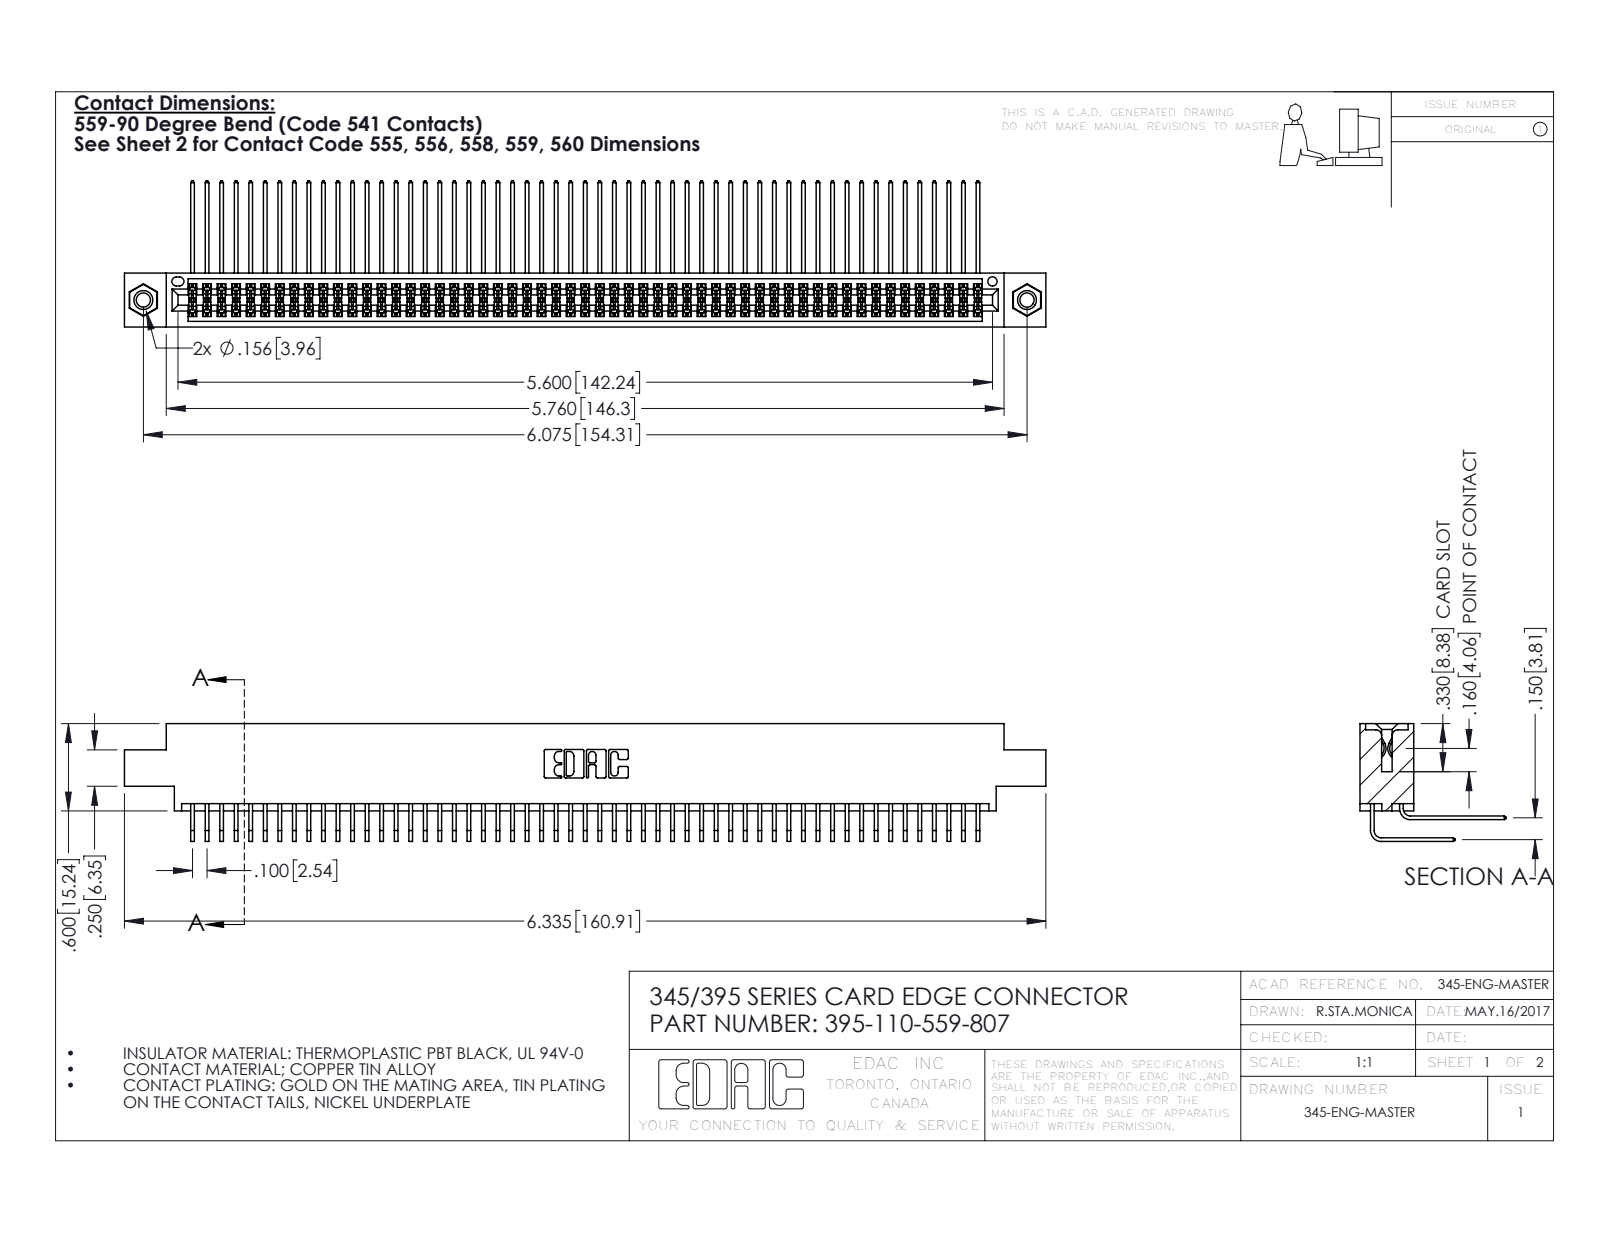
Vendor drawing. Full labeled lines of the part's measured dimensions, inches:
Part name (STEP PRODUCT): 345-292-001_559 Tail - 2; 345-292-001_558 559 Tail - 1; 395-110-559-807; 345 Part_0.170 Offset - 0.156 Dia-TI (+1 more)
STEP written by: SolidWorks 2016 (CONFIG_CONTROL_DESIGN)
Units: inches
Bodies: 113 solids, 5910 faces (3966 planar, 1928 cylindrical, 16 other)
Overall size (bounding box): 6.335 × 1.005 × 0.809
Volume: 0.992 in³ · Surface area: 42.53 in²
Round holes (diameter × count): ⌀0.098 ×2, ⌀0.125 ×2, ⌀0.156 ×2, ⌀0.064 ×1
Round bosses / shafts (diameter × count): ⌀0.155 ×2
Partial cylindrical surfaces — rounded edges, fillets, slot ends (radius × count): R0.006 ×165, R0.01 ×22, R0.007 ×6, R0.031 ×6, R0.026 ×3, R0.014 ×2, R0.019 ×2, R0.022 ×2
Main face-to-face distances: 0.072, 0.298, 0.37, 0.2, 0.098, 0.272, 0.025, 0.225, 0.175, 0.15
Hole centre spacings: 0.27, 5.839, 6.075
